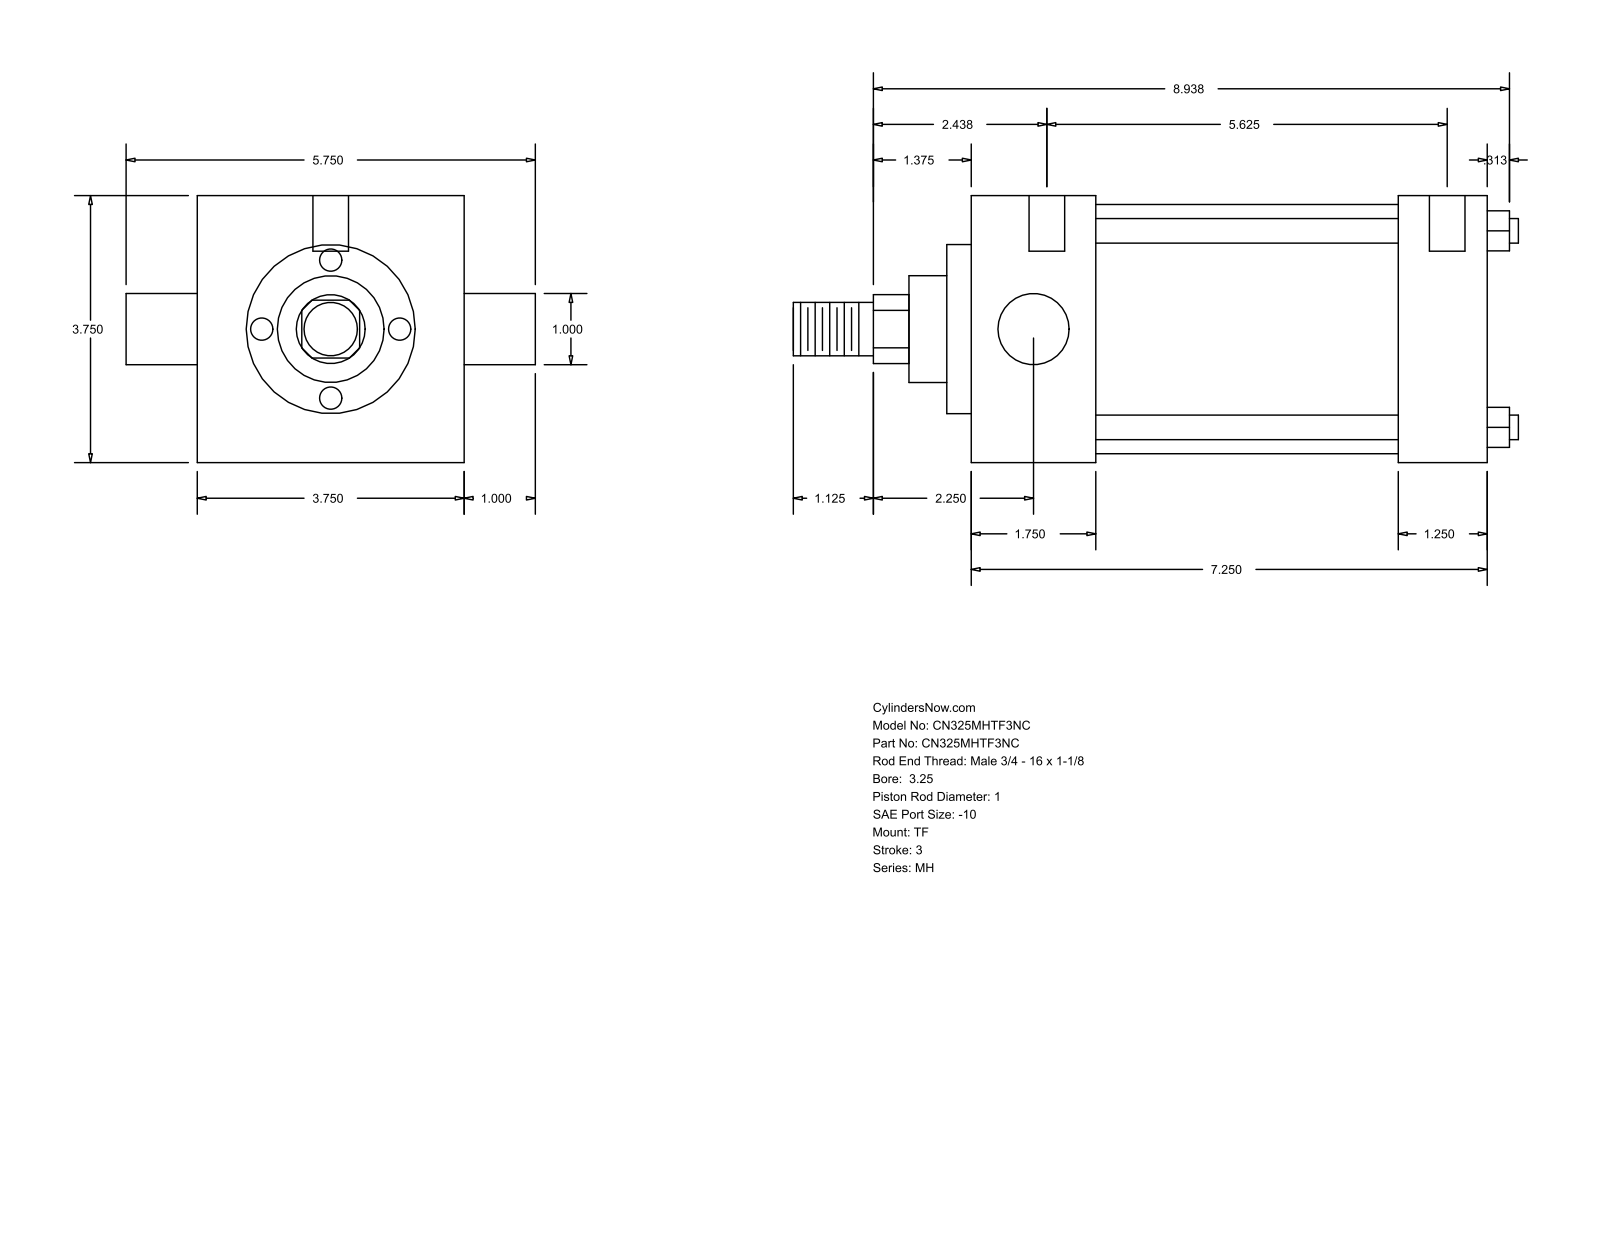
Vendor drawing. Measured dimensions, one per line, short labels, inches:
name: MH_TF__0325_1
written by: GSSL Pune (CONFIG_CONTROL_DESIGN)
unit: in
bodies: 0 solids, 86 faces (61 planar, 25 cylindrical, 0 other)
size: 10.187 × 5.75 × 3.75
holes: 3× ⌀0.219, 2× ⌀0.5
bosses: 4× ⌀0.345, 2× ⌀1, 1× ⌀3.5, 1× ⌀2.375, 1× ⌀1.5, 1× ⌀0.75
rounds: 1× R0.484
face distances: 3.75, 7.25, 1.75, 6, 4.25, 5.5, 1.25, 0.344, 2.094, 6.344
hole spacings: 0.062, 0.187, 5.625, 5.687, 5.813, 5.875
